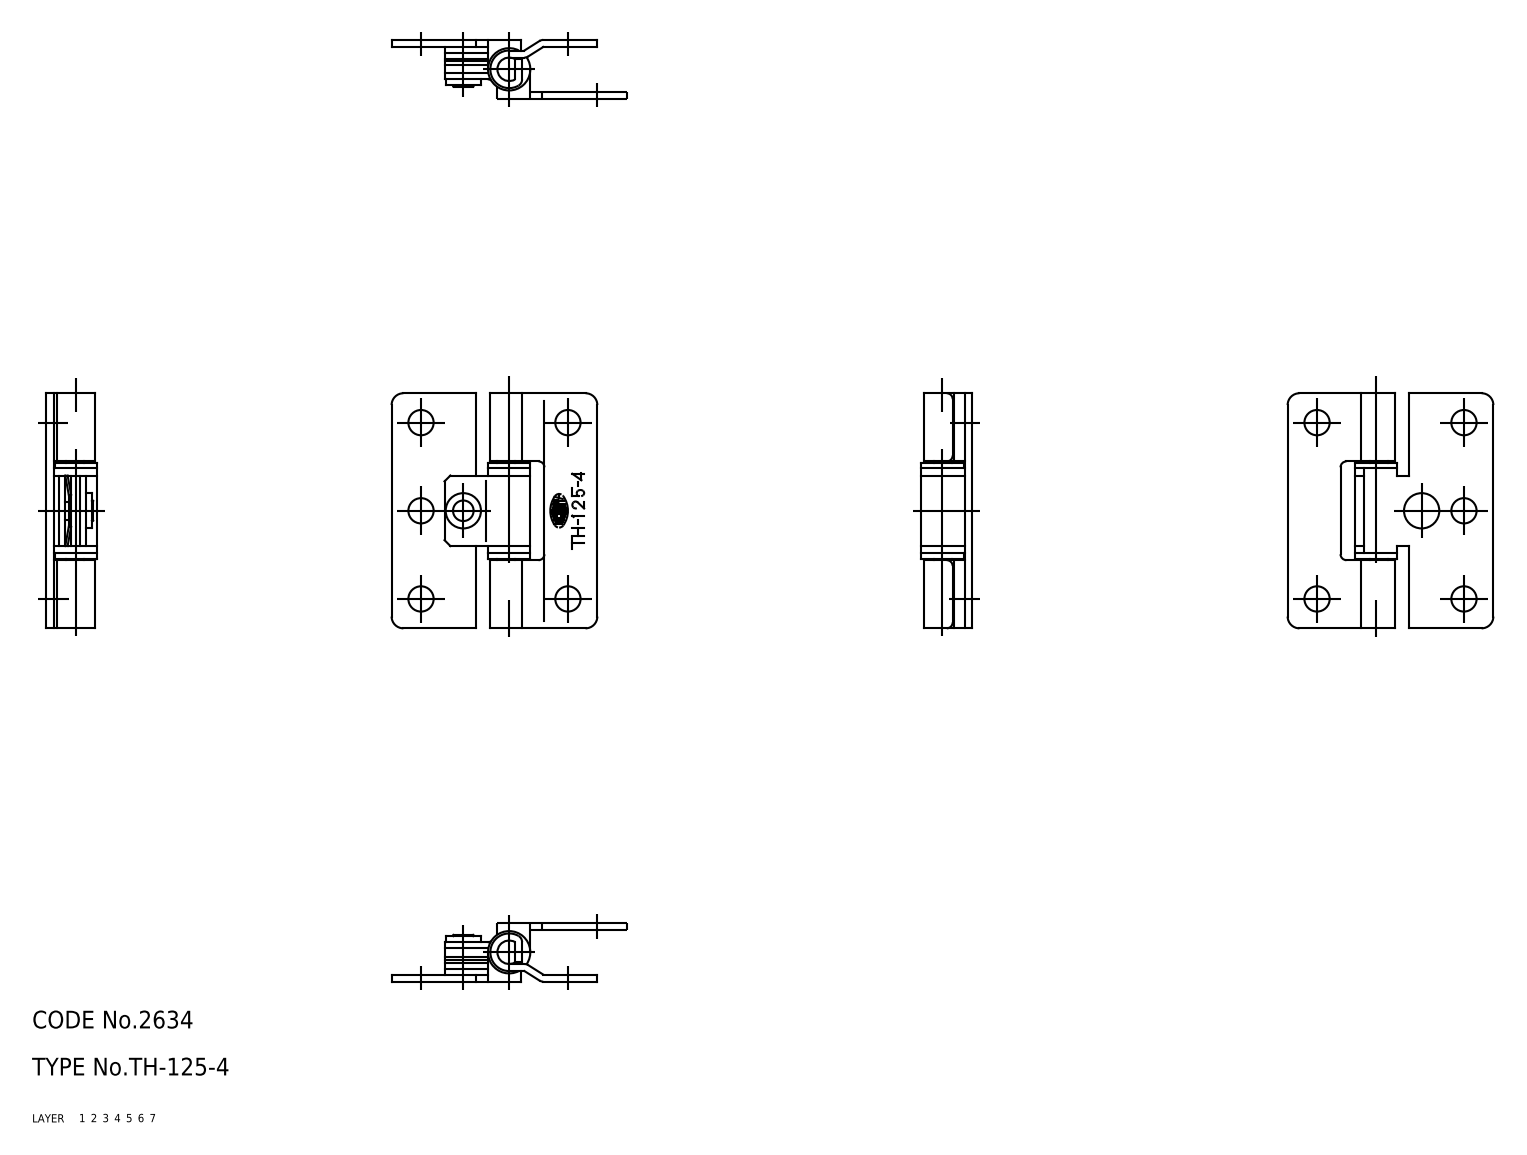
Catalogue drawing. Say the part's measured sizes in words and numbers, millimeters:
The part is named "67117556; 67117569; 67117582; 67117595 (+6 more)". Its 3-D file was written by "CADfix (AUTOMOTIVE_DESIGN)". It is 10 solids with 167 faces: 0 planar, 0 cylindrical and 167 other. Overall it measures 40 by 35 by 8.6 millimeters. Its volume is 3 068 cubic millimeters and its surface area 6 210 square millimeters.
